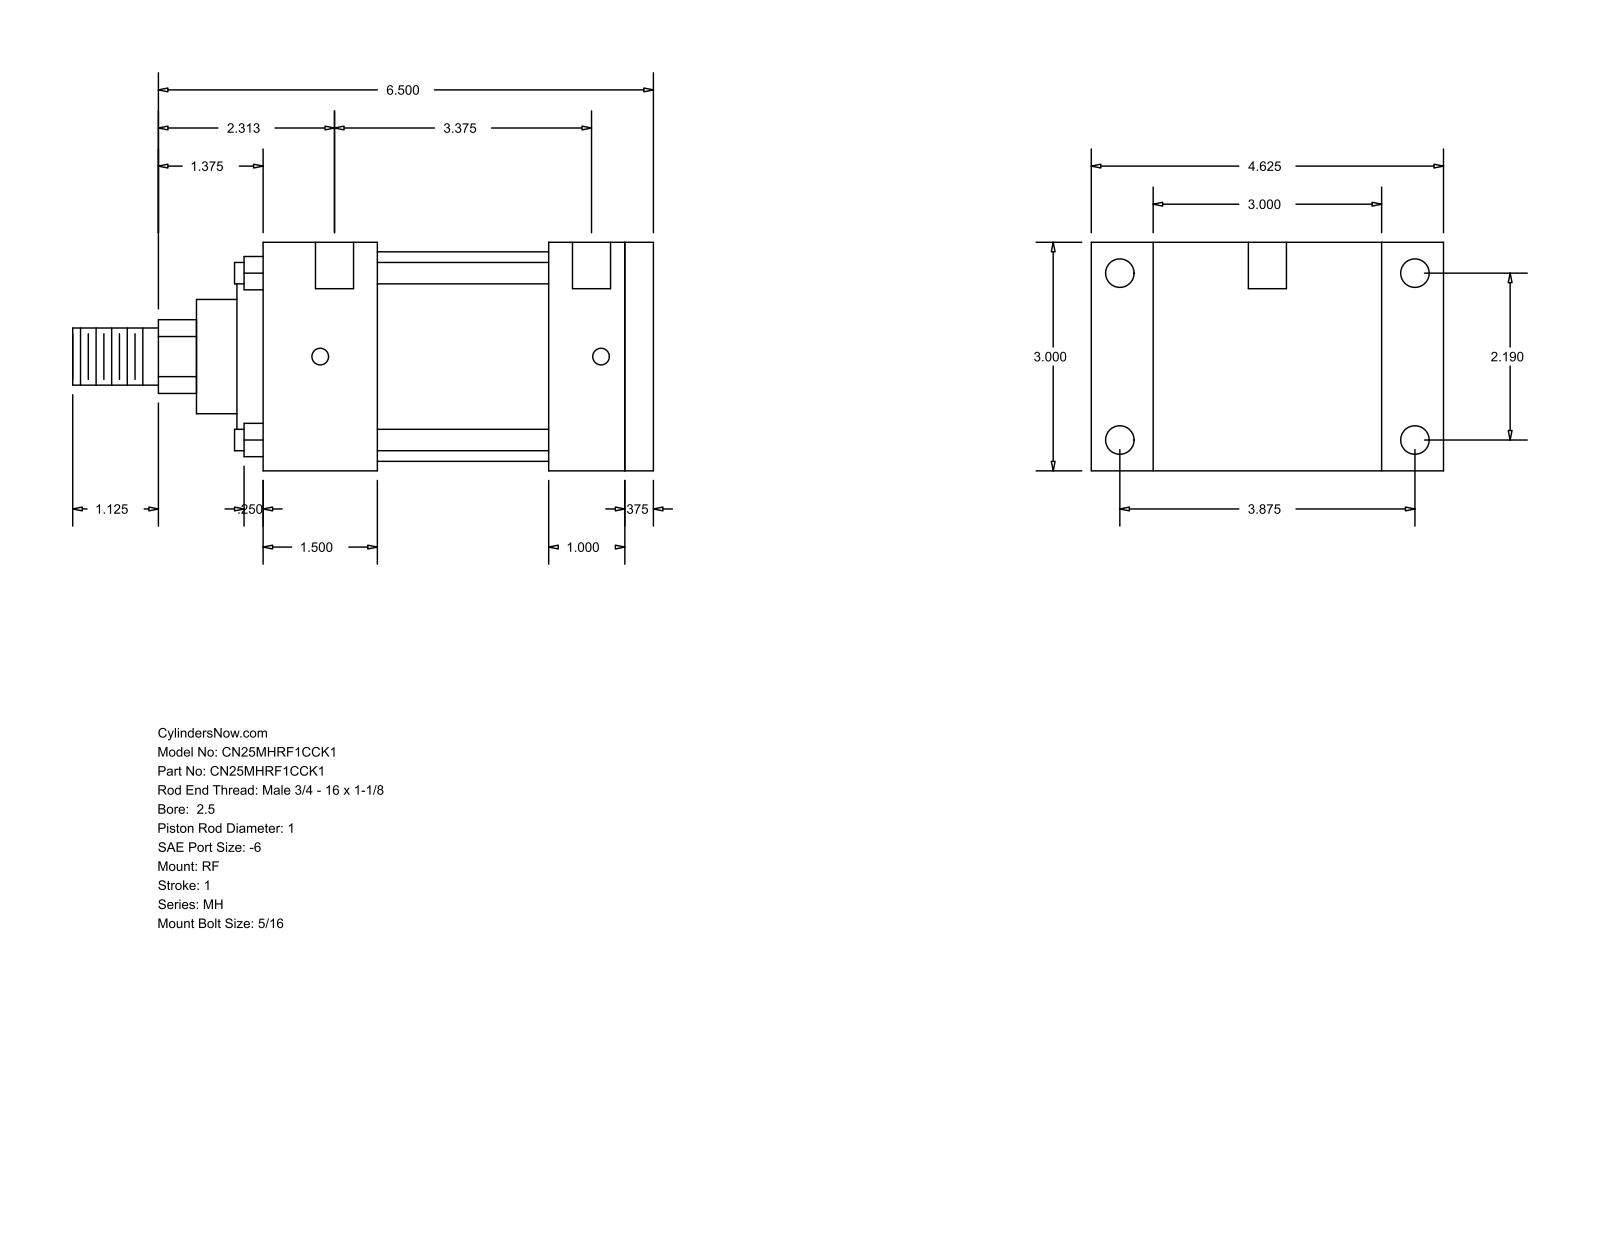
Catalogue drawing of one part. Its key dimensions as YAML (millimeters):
part_name: "MH_RF__0250_1"
step_written_by: "GSSL Pune (CONFIG_CONTROL_DESIGN)"
units: millimeters
bodies: {solids: 0, faces: 94, planar: 65, cylindrical: 29, other: 0}
overall_size: [193.68, 117.47, 76.2]
round_holes:
  - {diameter: 5.56, count: 4}
  - {diameter: 9.53, count: 4}
  - {diameter: 12.7, count: 2}
round_bosses_or_shafts:
  - {diameter: 7.14, count: 4}
  - {diameter: 69.85, count: 1}
  - {diameter: 60.33, count: 1}
  - {diameter: 38.1, count: 1}
  - {diameter: 25.4, count: 1}
  - {diameter: 19.05, count: 1}
partial_cylinders:
  - {radius: 12.29, count: 1}
face_to_face_distances: [76.2, 9.53, 130.18, 120.65, 34.92, 25.39, 95.26, 38.11, 57.15, 82.54]
hole_center_spacings: [55.62, 93.66, 98.42, 113.05, 3.18, 4.76, 85.72, 88.9]
